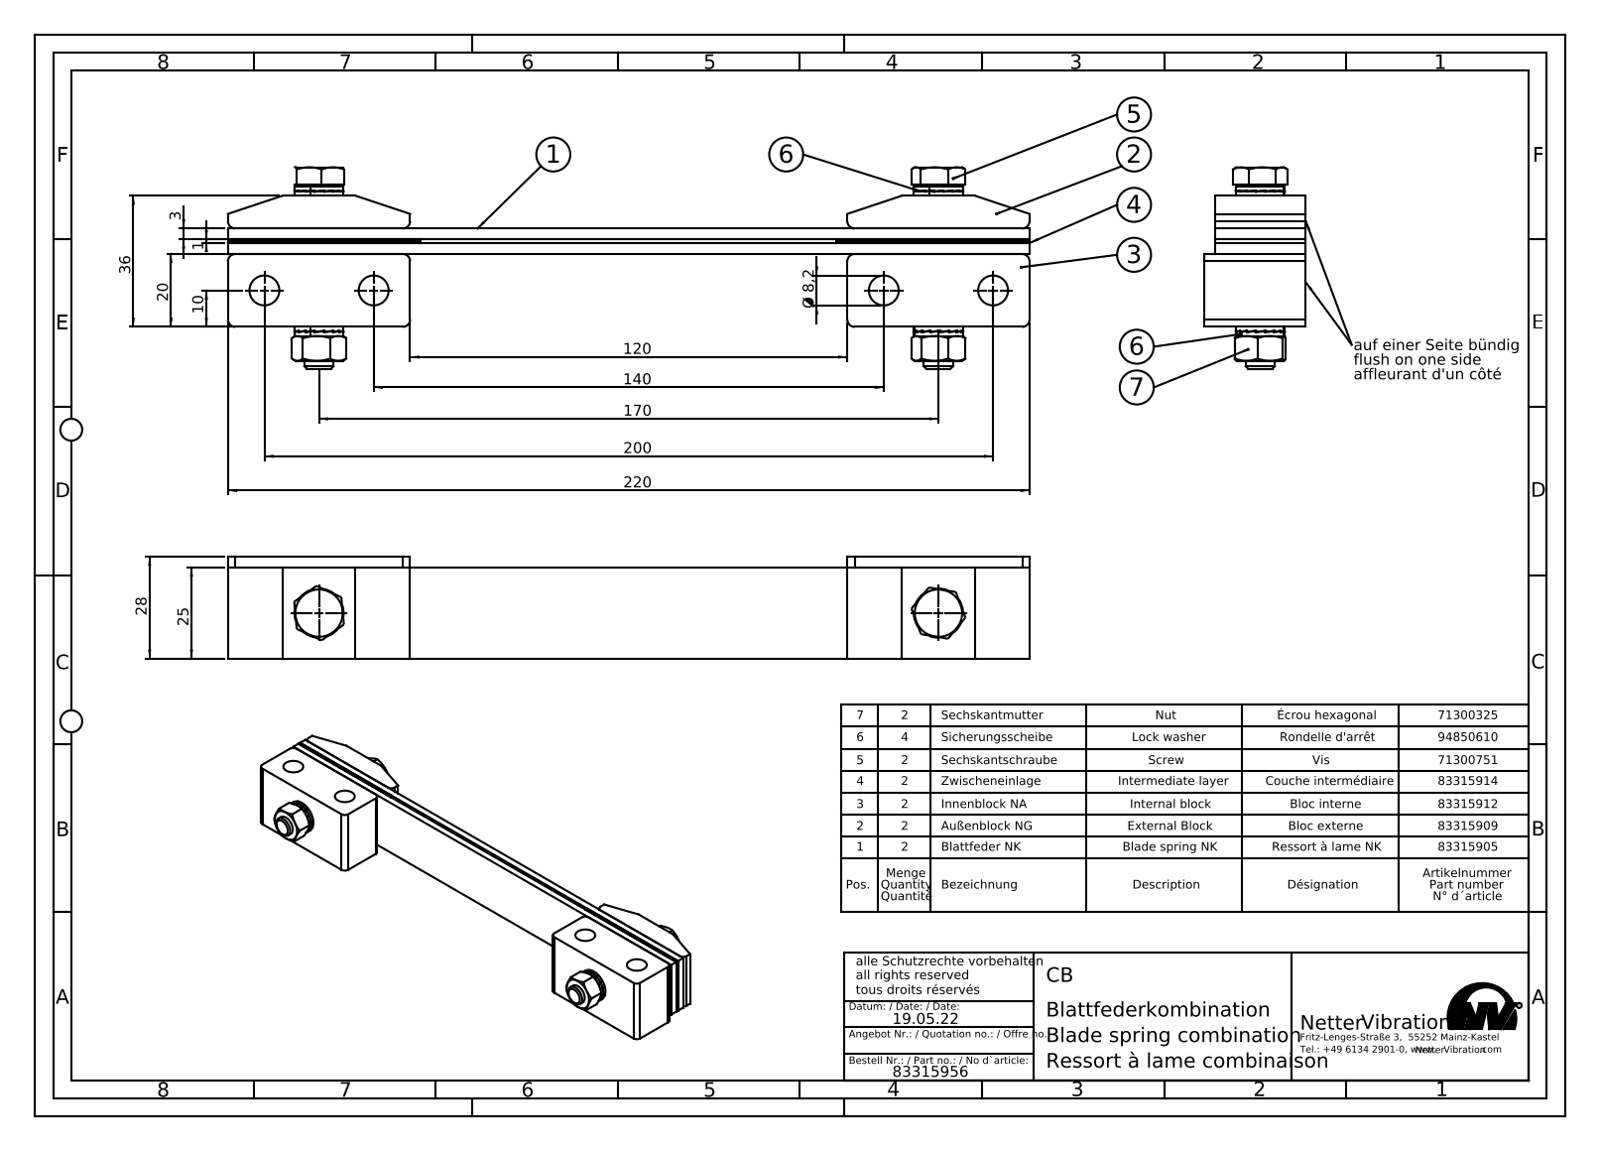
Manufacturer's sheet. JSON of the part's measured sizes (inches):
{"part_name": "Blattfederkombination CB # 83315956", "step_written_by": "SolidWorks 2015 (AUTOMOTIVE_DESIGN)", "units": "inches", "bodies": {"solids": 16, "faces": 686, "planar": 554, "cylindrical": 80, "other": 52}, "overall_size": [8.661, 2.177, 1.102], "volume_in3": 6.664, "surface_area_in2": 90.95, "round_holes": [[0.323, 6], [0.268, 2], [0.315, 2], [0.335, 2], [0.343, 2]], "round_bosses_or_shafts": [[0.531, 2], [0.512, 2]], "partial_cylinders_radius": [[0.079, 12]], "face_to_face_distances": [0.118, 0.157, 0.039, 0.276, 1.063, 0.945, 0.906, 0.787, 0.984, 1.102], "hole_center_spacings": [6.693, 1.181, 5.512, 7.874]}
